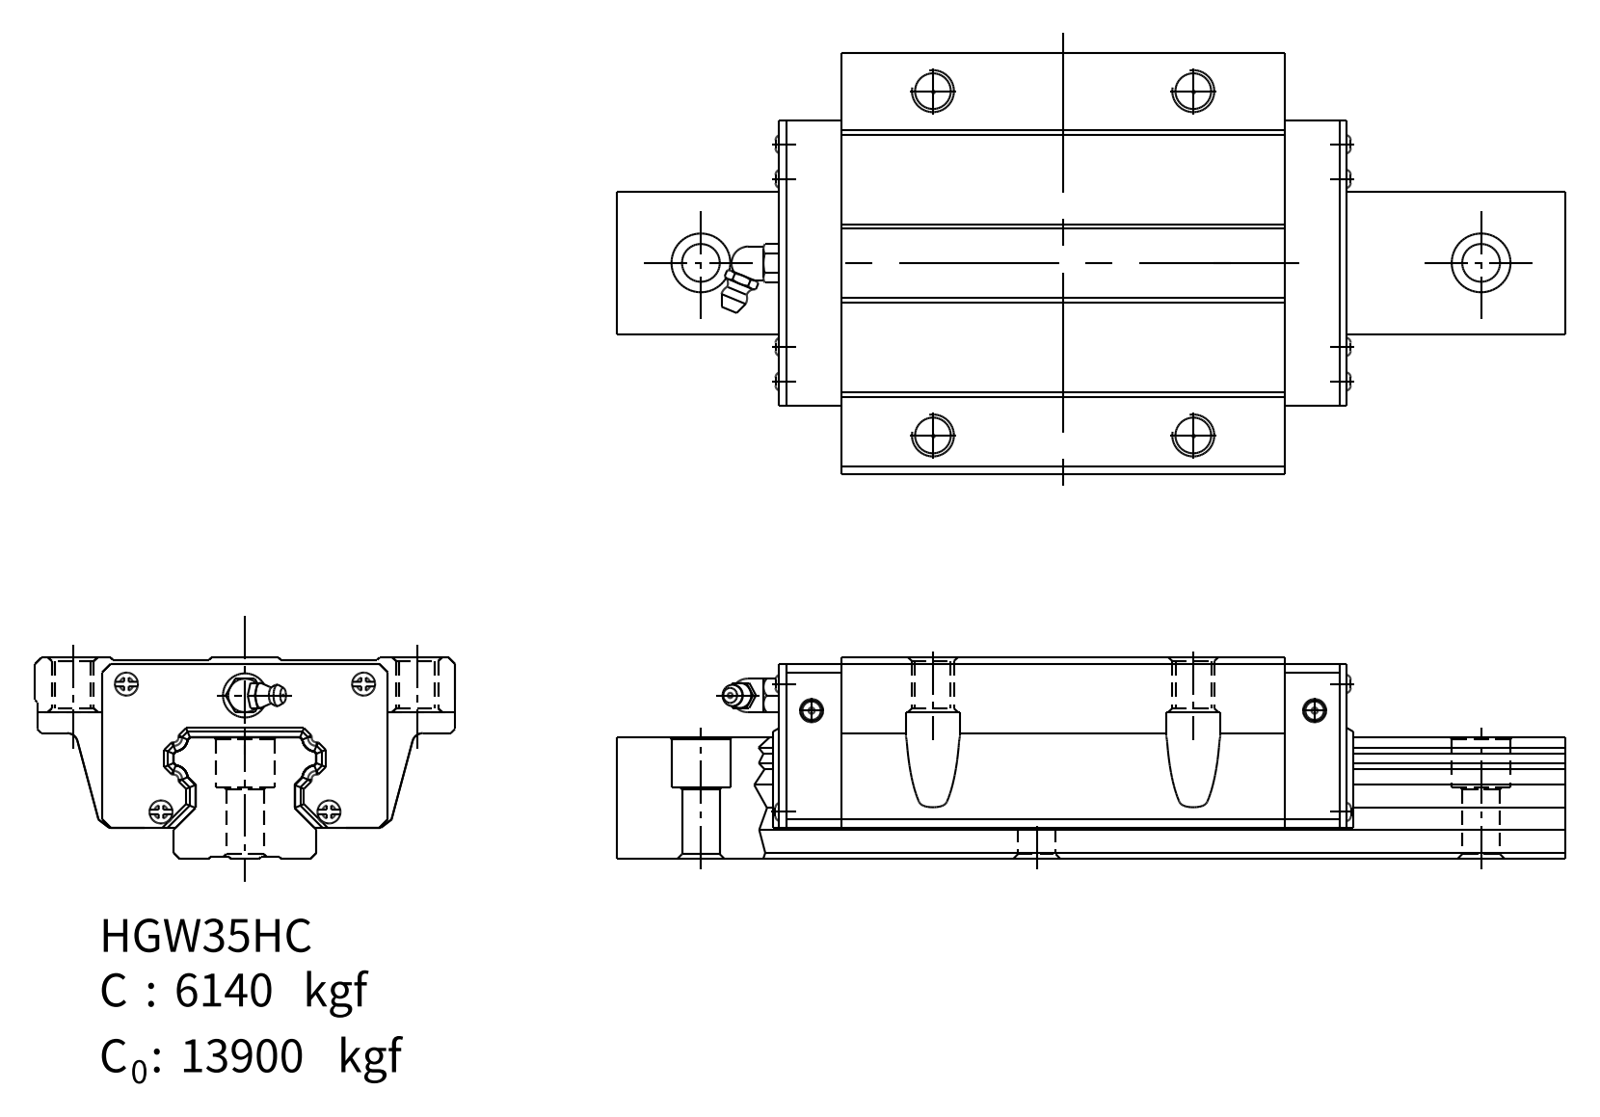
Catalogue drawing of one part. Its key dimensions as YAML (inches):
part_name: "HGW35HC"
step_written_by: "SolidWorks 2006104 (CONFIG_CONTROL_DESIGN)"
units: inches
bodies: {solids: 1, faces: 409, planar: 323, cylindrical: 26, other: 60}
overall_size: [5.453, 3.937, 1.594]
volume: 21.8
surface_area: 76.65
round_holes:
  - {diameter: 0.394, count: 4}
partial_cylinders:
  - {radius: 0.047, count: 4}
  - {radius: 0.128, count: 4}
  - {radius: 0.276, count: 4}
  - {radius: 0.098, count: 2}
face_to_face_distances: [0.02, 1.575, 1.594, 0.846, 0.728, 0.748, 5.441, 0.057, 0.037, 1.537]
hole_center_spacings: [2.441, 3.228, 4.047]
